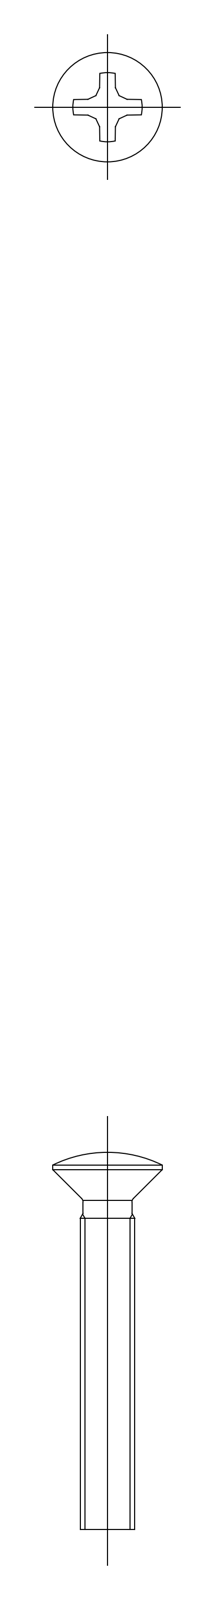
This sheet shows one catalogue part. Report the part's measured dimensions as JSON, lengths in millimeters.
{"part_name": "screw", "step_written_by": "CADfix (AUTOMOTIVE_DESIGN)", "units": "millimeters", "bodies": {"solids": 1, "faces": 27, "planar": 0, "cylindrical": 0, "other": 27}, "overall_size": [20.67, 6, 6], "volume_mm3": 166, "surface_area_mm2": 252}
